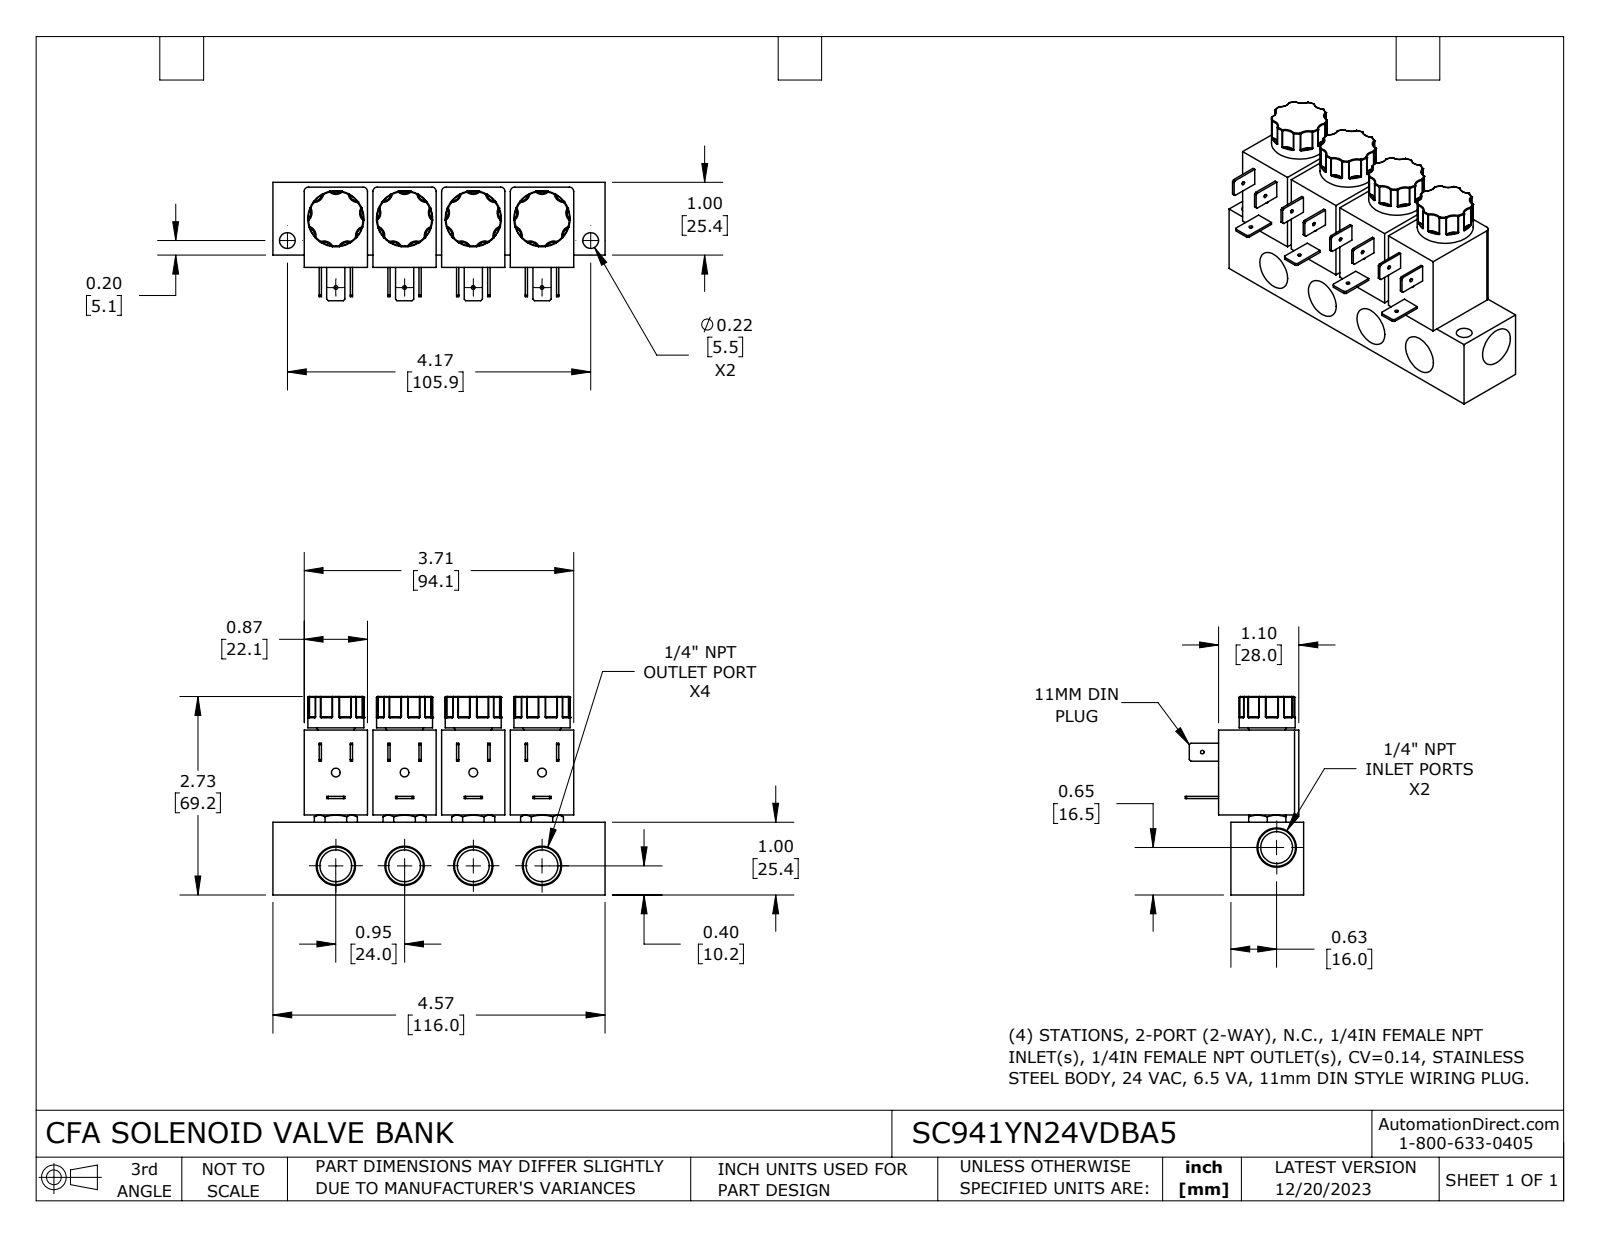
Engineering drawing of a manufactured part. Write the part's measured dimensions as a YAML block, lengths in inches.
part_name: "SC941YN24VDBA5"
step_written_by: "SolidWorks 2023 (CONFIG_CONTROL_DESIGN)"
units: inches
bodies: {solids: 1, faces: 868, planar: 192, cylindrical: 184, other: 492}
overall_size: [4.567, 2.725, 1.627]
volume: 9.182
surface_area: 61.05
round_holes:
  - {diameter: 0.05, count: 5}
  - {diameter: 0.438, count: 5}
  - {diameter: 0.12, count: 4}
  - {diameter: 0.217, count: 2}
round_bosses_or_shafts:
  - {diameter: 0.77, count: 4}
partial_cylinders:
  - {radius: 0.01, count: 72}
  - {radius: 0.133, count: 34}
  - {radius: 0.06, count: 8}
  - {radius: 0.132, count: 2}
face_to_face_distances: [1, 0.945, 1.169, 1.89, 1.815, 0.87, 0.169, 0.065, 0.935, 1.104]
hole_center_spacings: [0.945, 1.282, 1.593, 0.945, 1.89, 1.89, 2.835, 1.593]
